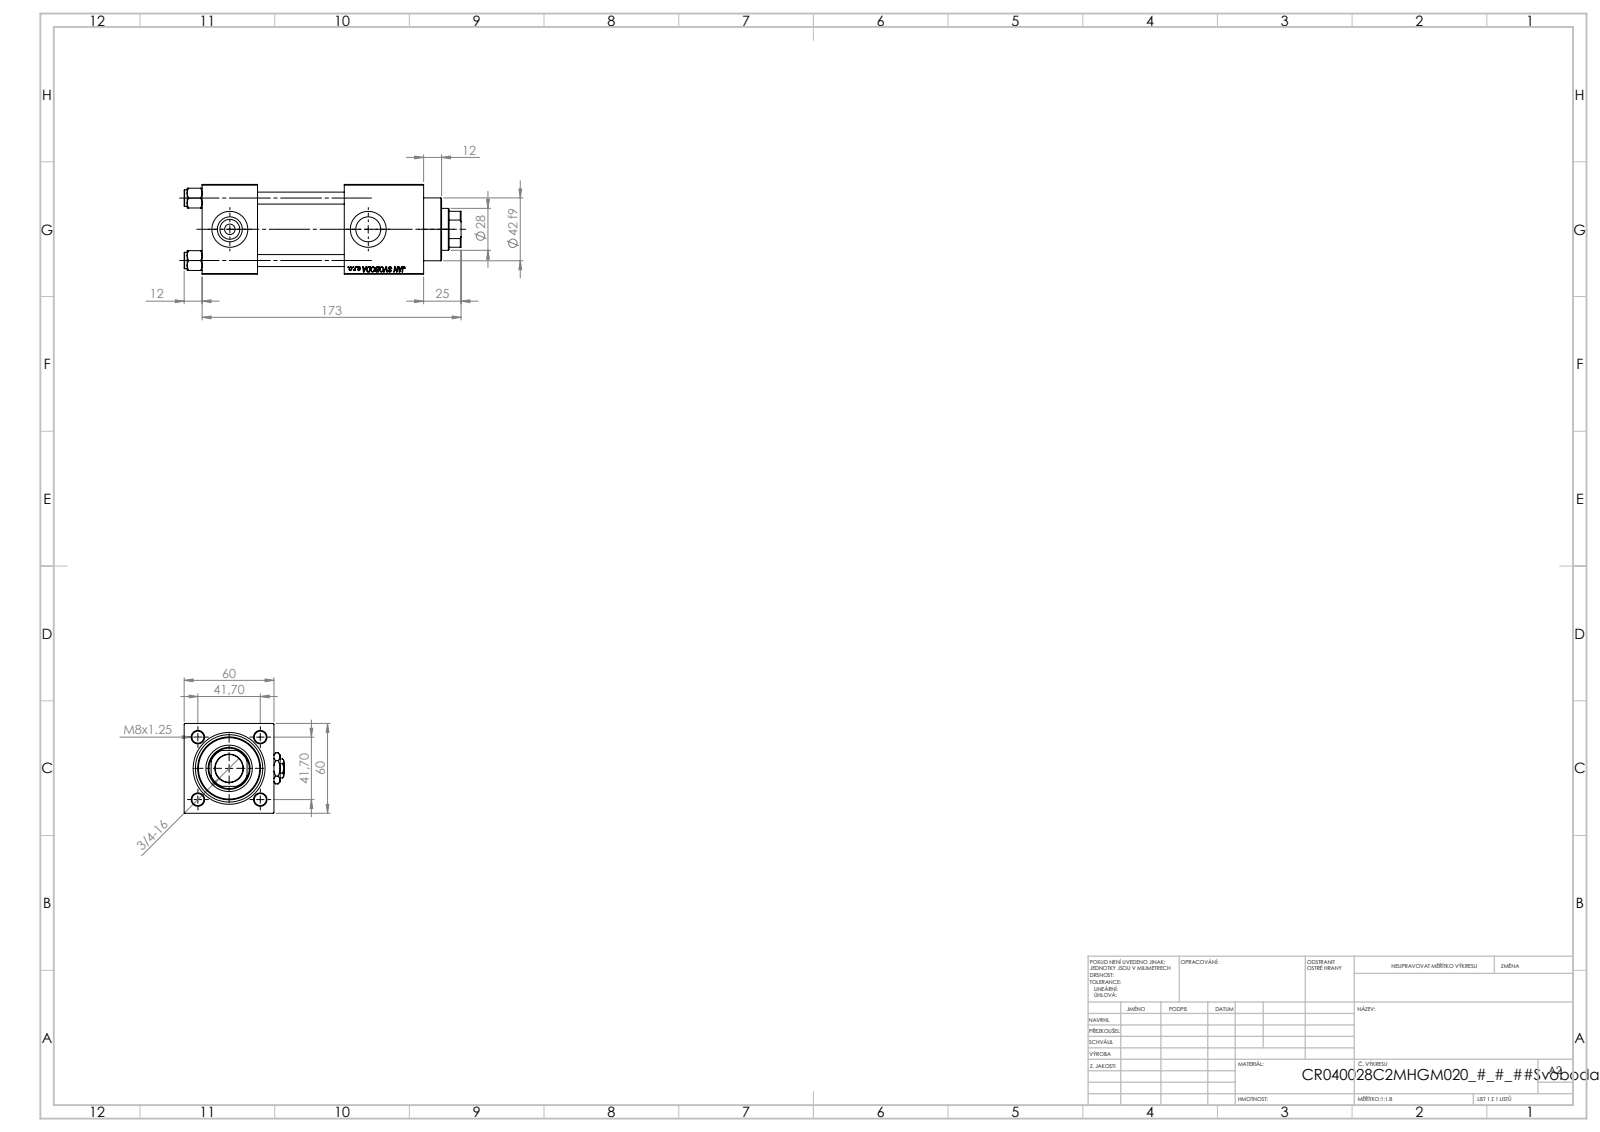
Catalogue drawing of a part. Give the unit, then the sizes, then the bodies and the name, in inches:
Units: inches
Overall size (bounding box): 7.283 × 2.638 × 2.362
Round holes (diameter × count): ⌀0.315 ×4, ⌀0.276 ×2, ⌀0.656 ×2, ⌀0.945 ×2, ⌀0.728 ×1, ⌀1.102 ×1, ⌀1.22 ×1, ⌀1.575 ×1, ⌀1.772 ×1
Round bosses / shafts (diameter × count): ⌀0.433 ×4, ⌀1.811 ×1, ⌀1.654 ×1
Partial cylindrical surfaces — rounded edges, fillets, slot ends (radius × count): R0.531 ×1
Main face-to-face distances: 2.362, 1.457, 2.283, 3.74, 2.087, 4.697, 3.24, 0.957, 5.827, 4.37
Hole centre spacings: 1.161, 1.642, 2.322, 3.642
Volume: 25.8 in³ · Surface area: 175.3 in²
Bodies: 12 solids, 1202 faces (550 planar, 94 cylindrical, 558 other)
Part name (STEP PRODUCT): NUT_M5_C; V215CR_C_Body; Zatka_pro_OIL_PORT; V215_VC_A (+2 more)
STEP written by: SolidWorks 2019 (CONFIG_CONTROL_DESIGN)
